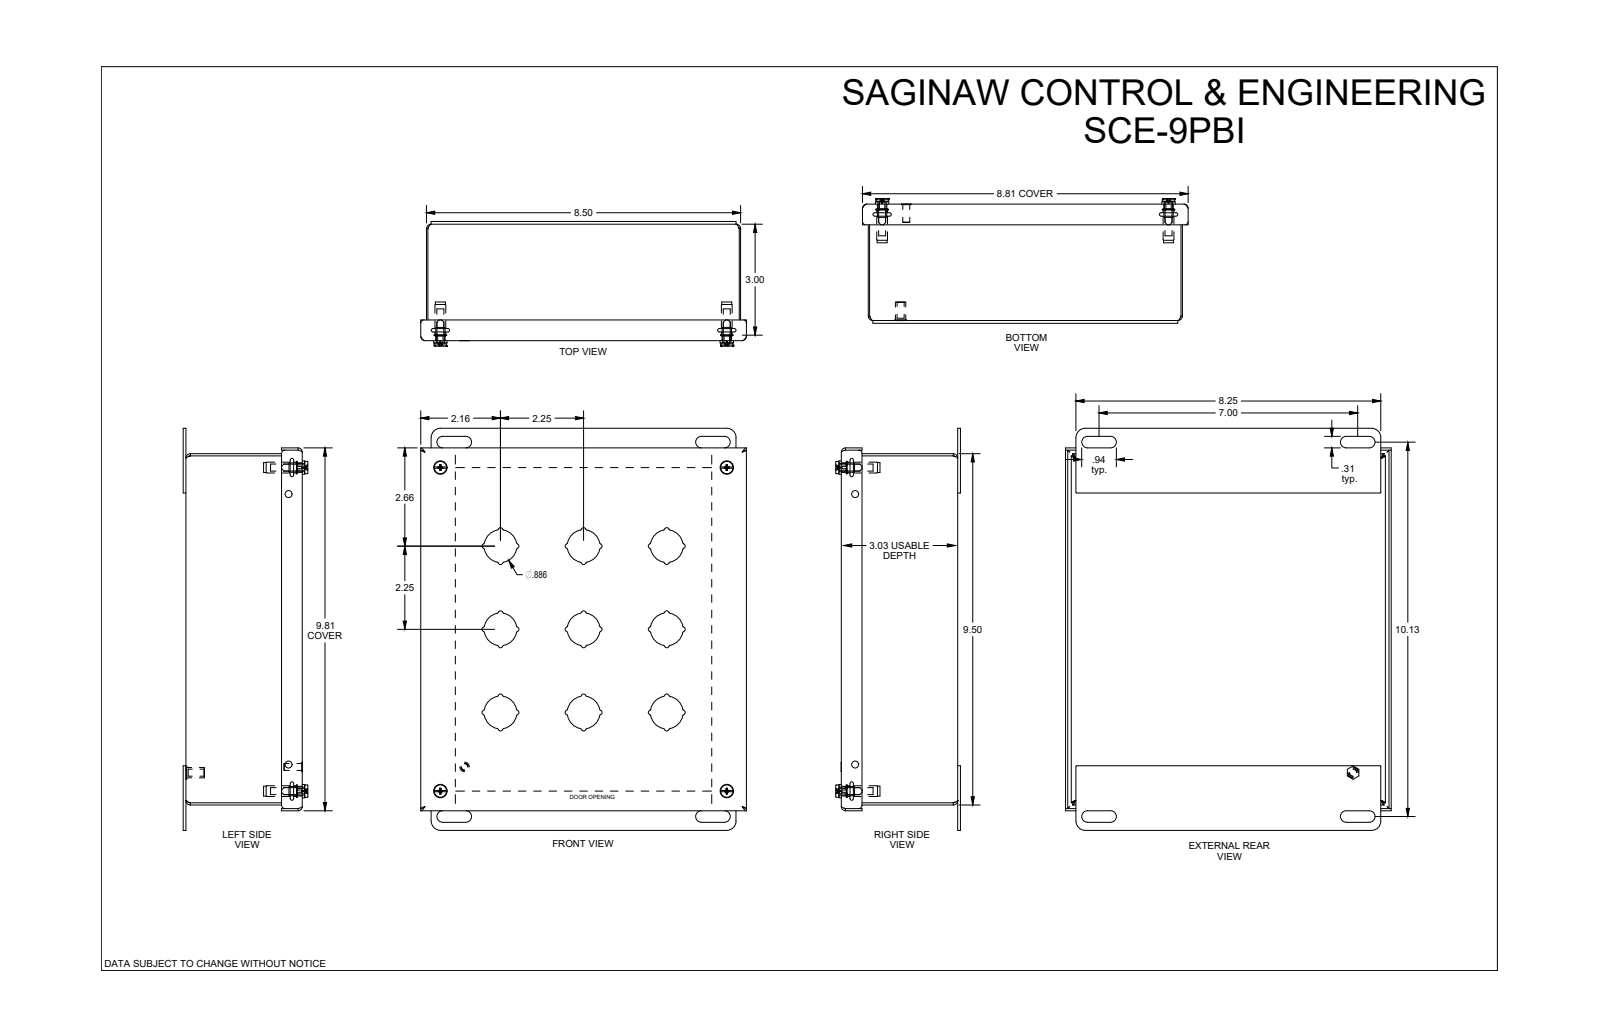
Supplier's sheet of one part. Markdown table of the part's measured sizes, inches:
| quantity | value |
| --- | --- |
| part name | SCE-9PBI |
| STEP written by | SolidWorks 2024 (AUTOMOTIVE_DESIGN) |
| units | inches |
| bodies | 15 solids, 506 faces (154 planar, 300 cylindrical, 52 other) |
| overall size | 10.875 × 8.813 × 3.286 |
| volume | 20.97 in³ |
| surface area | 692.7 in² |
| round holes (diameter × count) | 0.19 × 5, 0.22 × 4, 0.25 × 4, 0.266 × 4, 0.317 × 4, 0.187 × 2 |
| round bosses / shafts (diameter × count) | 0.362 × 4, 0.34 × 4, 0.292 × 4, 0.27 × 4, 0.26 × 4, 0.28 × 1, 0.256 × 1, 0.188 × 1 |
| partial cylindrical surfaces (radius × count) | 0.04 × 72, 0.062 × 27, 0.063 × 9, 0.443 × 9, 0.015 × 8, 0.058 × 8, 0.115 × 8, 0.118 × 8 |
| main face-to-face distances | 0.06, 3.088, 3.148, 3.028, 8.44, 9.44, 0.156, 2.94, 0.148, 0.075 |
| hole center spacings | 7.75, 8.75, 11.688, 0.707, 7.267, 7.313, 8.265, 10.983 |
